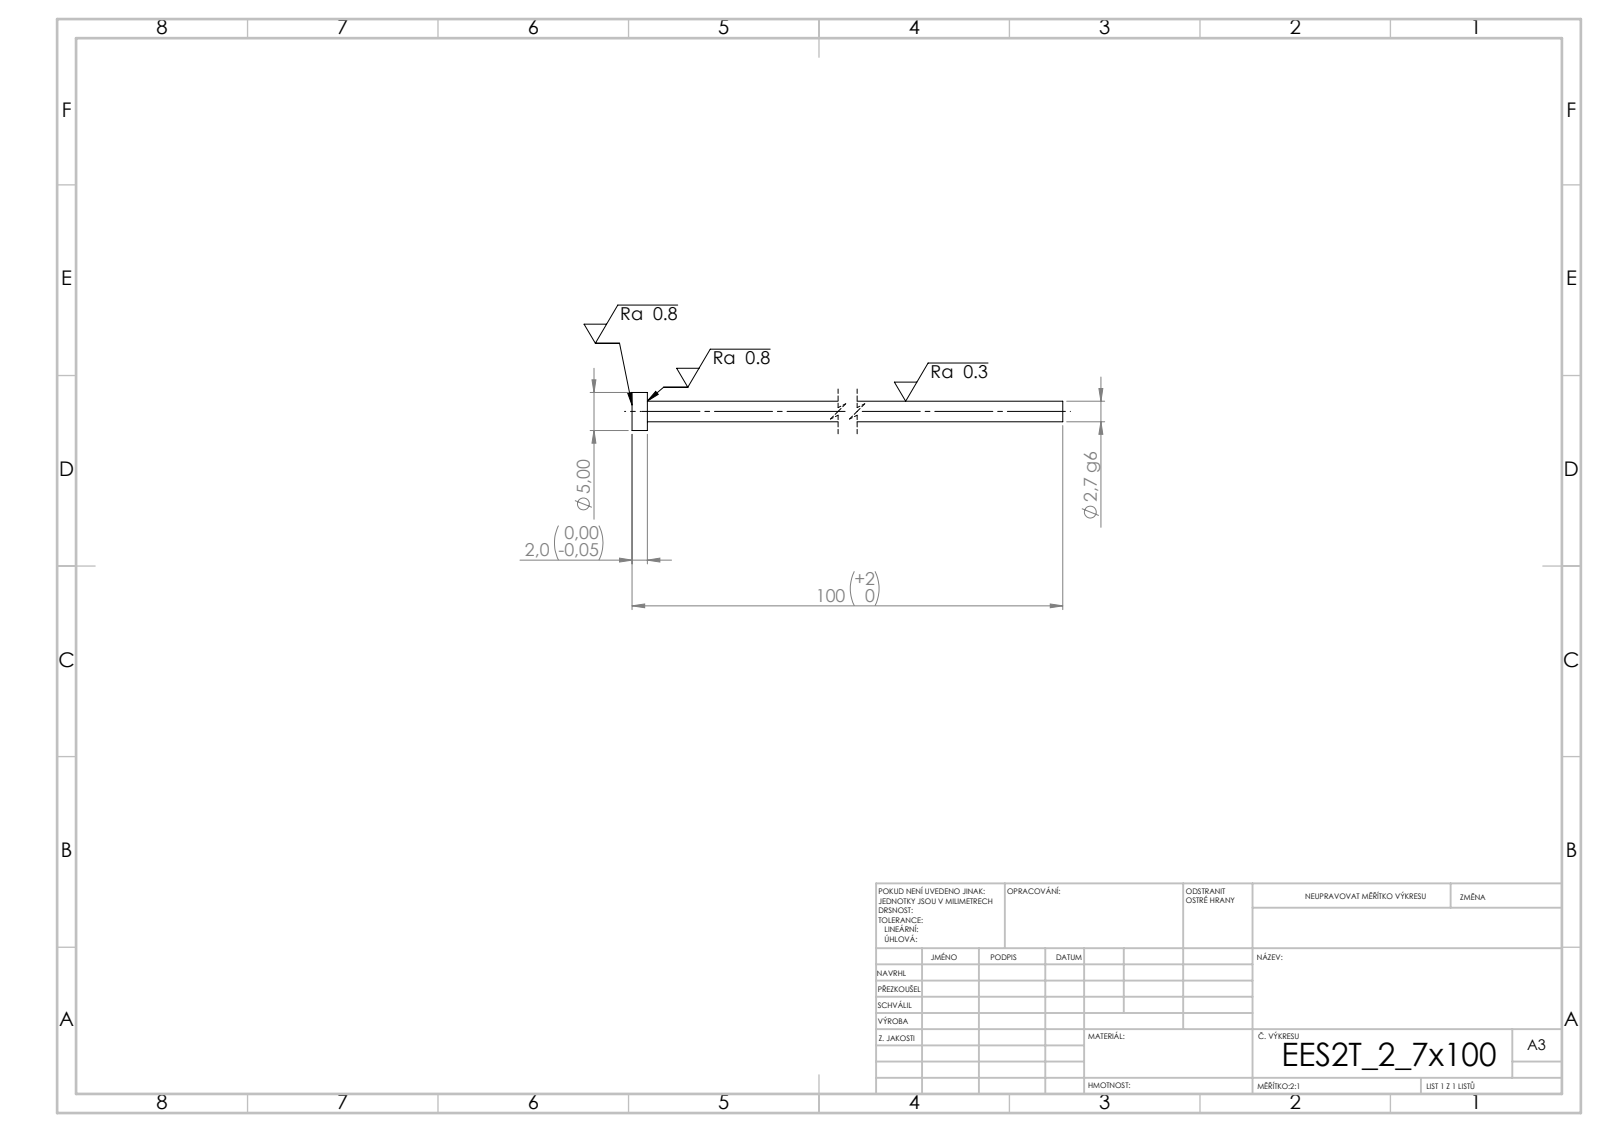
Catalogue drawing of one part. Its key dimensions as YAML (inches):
step_written_by: "SolidWorks 2019 (CONFIG_CONTROL_DESIGN)"
units: inches
bodies: {solids: 1, faces: 7, planar: 3, cylindrical: 4, other: 0}
overall_size: [3.937, 0.197, 0.197]
volume: 0.037
surface_area: 1.4
round_bosses_or_shafts:
  - {diameter: 0.197, count: 1}
  - {diameter: 0.106, count: 1}
face_to_face_distances: [0.079, 3.937, 3.858]
